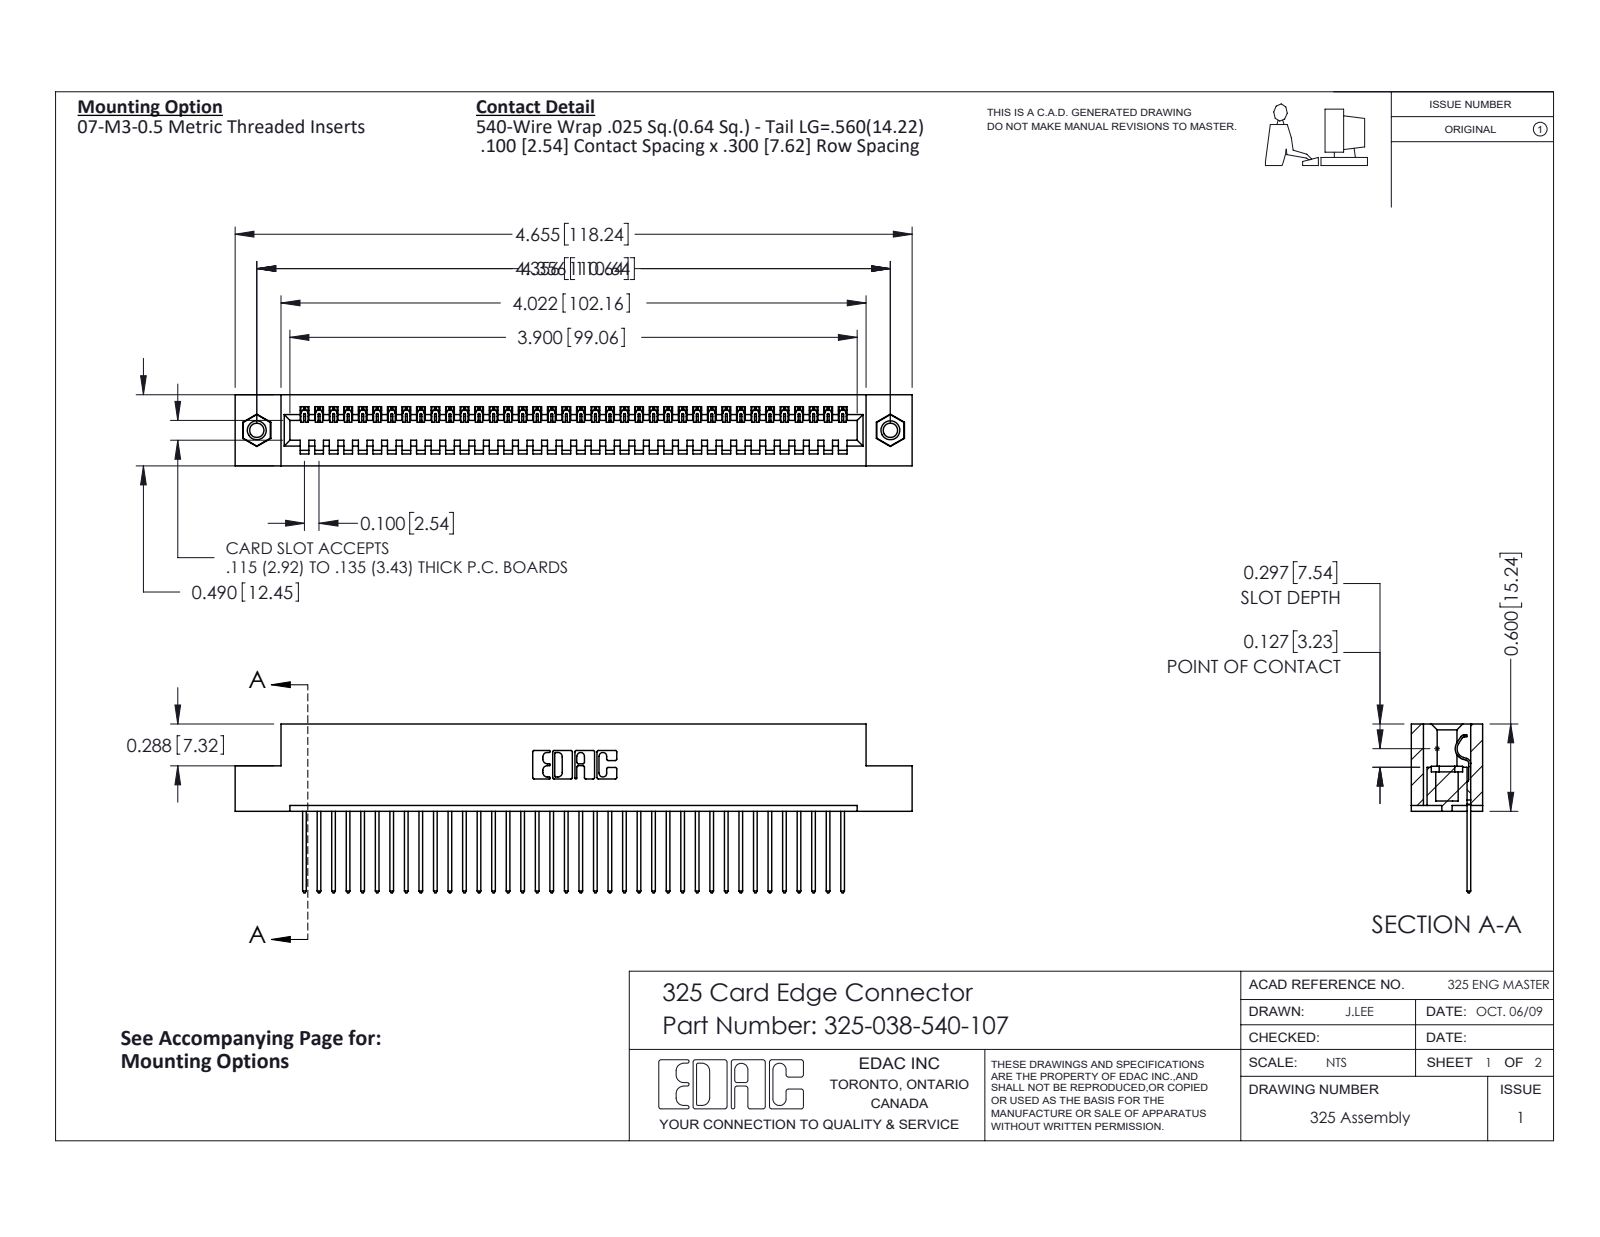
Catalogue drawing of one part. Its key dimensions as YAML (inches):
part_name: "345-250-001_345-250-005-103; 325-292-001_325-293-140; 325-038-540-107; 325 Part_TI"
step_written_by: "SolidWorks 2016 (CONFIG_CONTROL_DESIGN)"
units: inches
bodies: {solids: 41, faces: 2378, planar: 1698, cylindrical: 664, other: 16}
overall_size: [4.655, 1.16, 0.49]
volume: 0.916
surface_area: 25.96
round_holes:
  - {diameter: 0.098, count: 2}
  - {diameter: 0.125, count: 2}
  - {diameter: 0.16, count: 2}
round_bosses_or_shafts:
  - {diameter: 0.155, count: 2}
partial_cylinders:
  - {radius: 0.006, count: 76}
  - {radius: 0.01, count: 76}
  - {radius: 0.01, count: 22}
  - {radius: 0.007, count: 6}
  - {radius: 0.031, count: 6}
  - {radius: 0.026, count: 3}
  - {radius: 0.014, count: 1}
  - {radius: 0.022, count: 1}
face_to_face_distances: [0.083, 0.407, 0.49, 0.3, 0.107, 0.383, 0.025, 0.325, 0.56, 0.263]
hole_center_spacings: [4.356]
